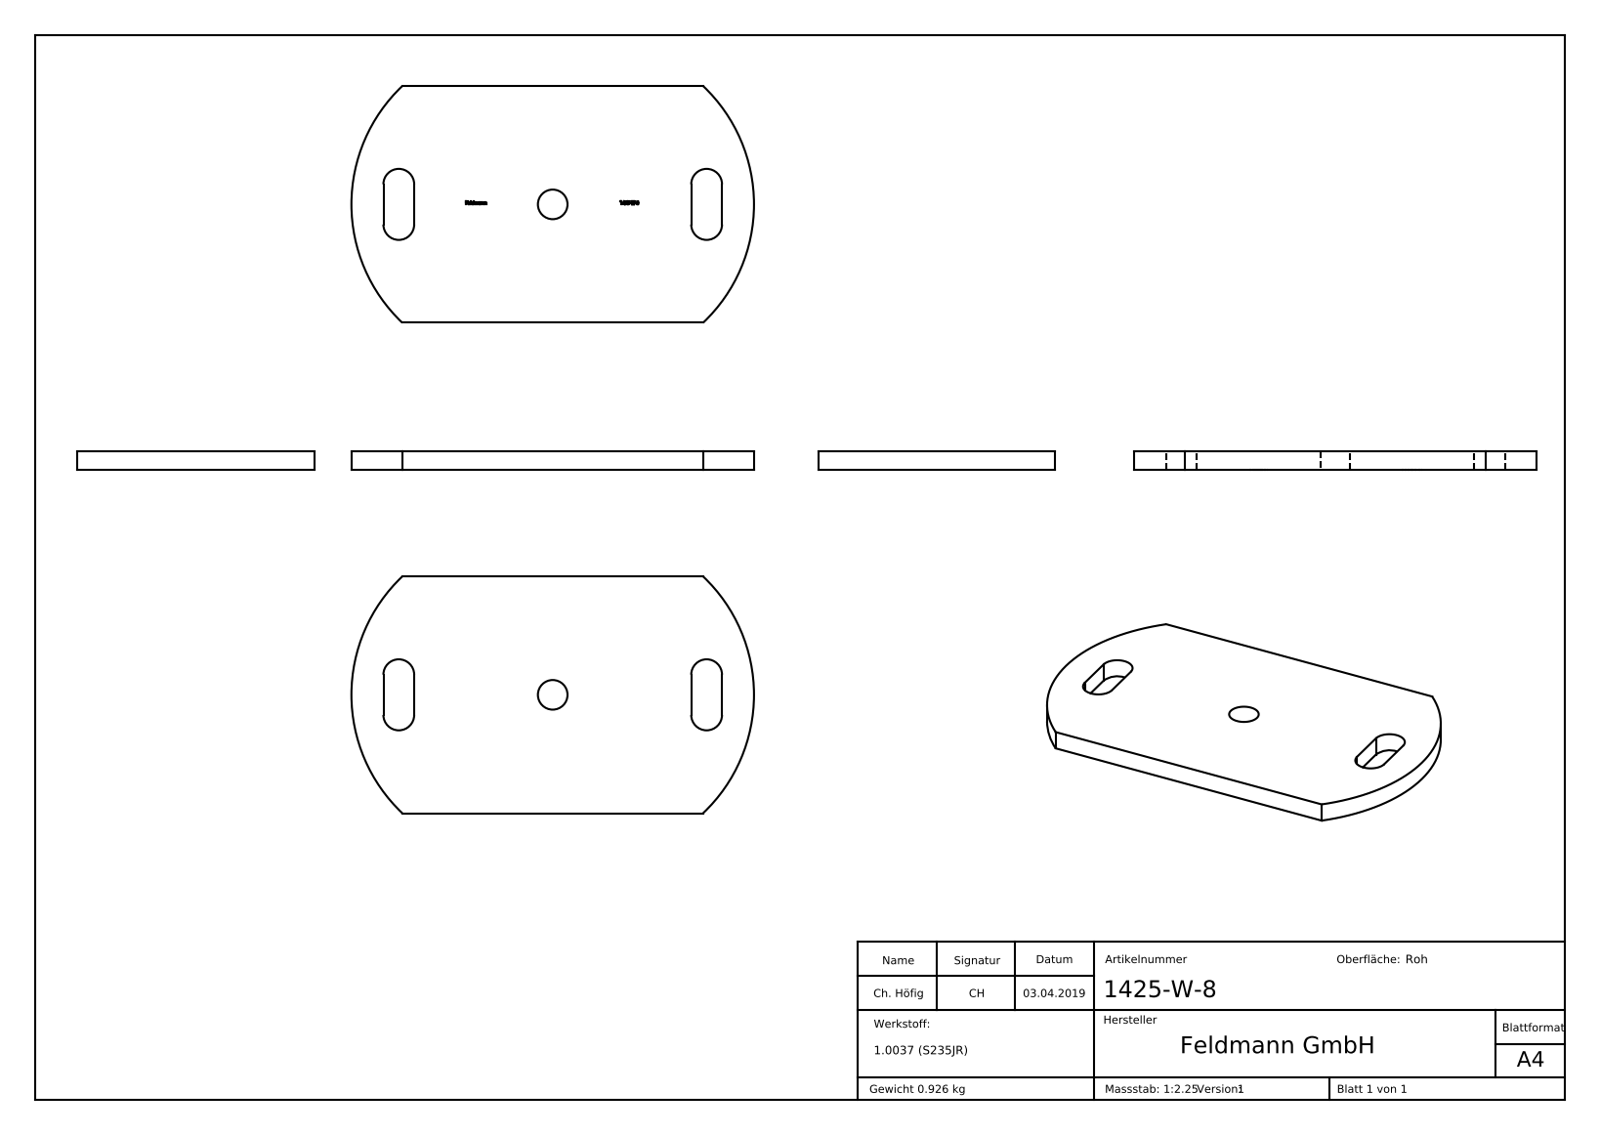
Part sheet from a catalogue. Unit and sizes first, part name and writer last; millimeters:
Units: millimetres
Overall size (bounding box): 170 × 100 × 8
Round holes (diameter × count): ⌀12.5 ×1
Partial cylindrical surfaces — rounded edges, fillets, slot ends (radius × count): R6.5 ×4, R68.89 ×2
Main face-to-face distances: 8, 100, 13, 130, 143, 117, 7.9, 50, 63.47, 0.44
Volume: 118 718 mm³ · Surface area: 35 023 mm²
Bodies: 1 solid, 225 faces (136 planar, 10 cylindrical, 79 other)
Part name (STEP PRODUCT): 1425-W-8
STEP written by: SolidWorks 2015 (CONFIG_CONTROL_DESIGN)
